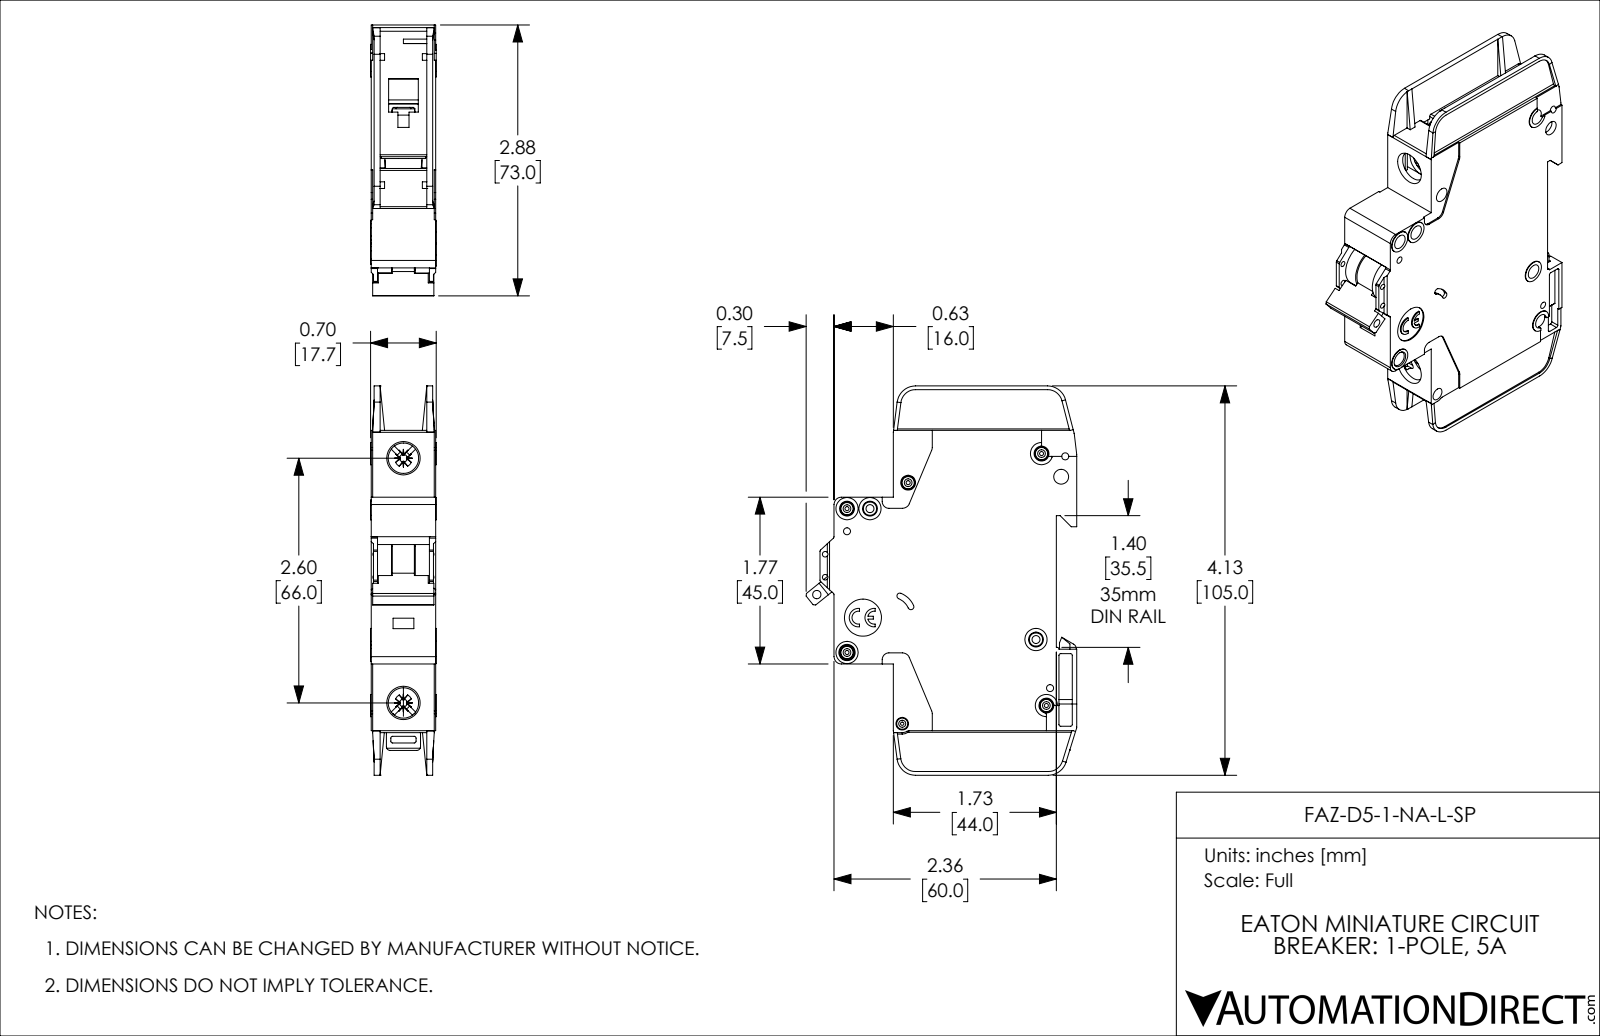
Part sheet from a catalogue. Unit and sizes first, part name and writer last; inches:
Units: inches
Overall size (bounding box): 4.134 × 2.876 × 0.697
Round holes (diameter × count): ⌀0.157 ×8, ⌀0.043 ×5, ⌀0.075 ×4, ⌀0.059 ×2, ⌀0.085 ×2, ⌀0.323 ×2, ⌀0.035 ×1, ⌀0.089 ×1, ⌀0.098 ×1, ⌀0.134 ×1, ⌀0.394 ×1
Round bosses / shafts (diameter × count): ⌀0.13 ×5, ⌀0.236 ×4, ⌀0.118 ×2, ⌀0.098 ×1
Partial cylindrical surfaces — rounded edges, fillets, slot ends (radius × count): R0.02 ×42, R0.016 ×10, R0.039 ×10, R0.079 ×8, R0.197 ×5, R0.008 ×4, R0.026 ×4, R0.043 ×4
Main face-to-face distances: 0.047, 0.685, 0.591, 0.638, 0.094, 0.543, 0.016, 0.031, 0.496, 0.575
Hole centre spacings: 0.244, 0.537, 0.87, 0.189, 0.199, 0.204, 0.221, 0.24
Volume: 4.682 in³ · Surface area: 41.01 in²
Bodies: 1 solid, 1127 faces (671 planar, 357 cylindrical, 99 other)
Part name (STEP PRODUCT): FAZ-D5-1-NA-L-SP
STEP written by: SolidWorks 2019 (AUTOMOTIVE_DESIGN)
